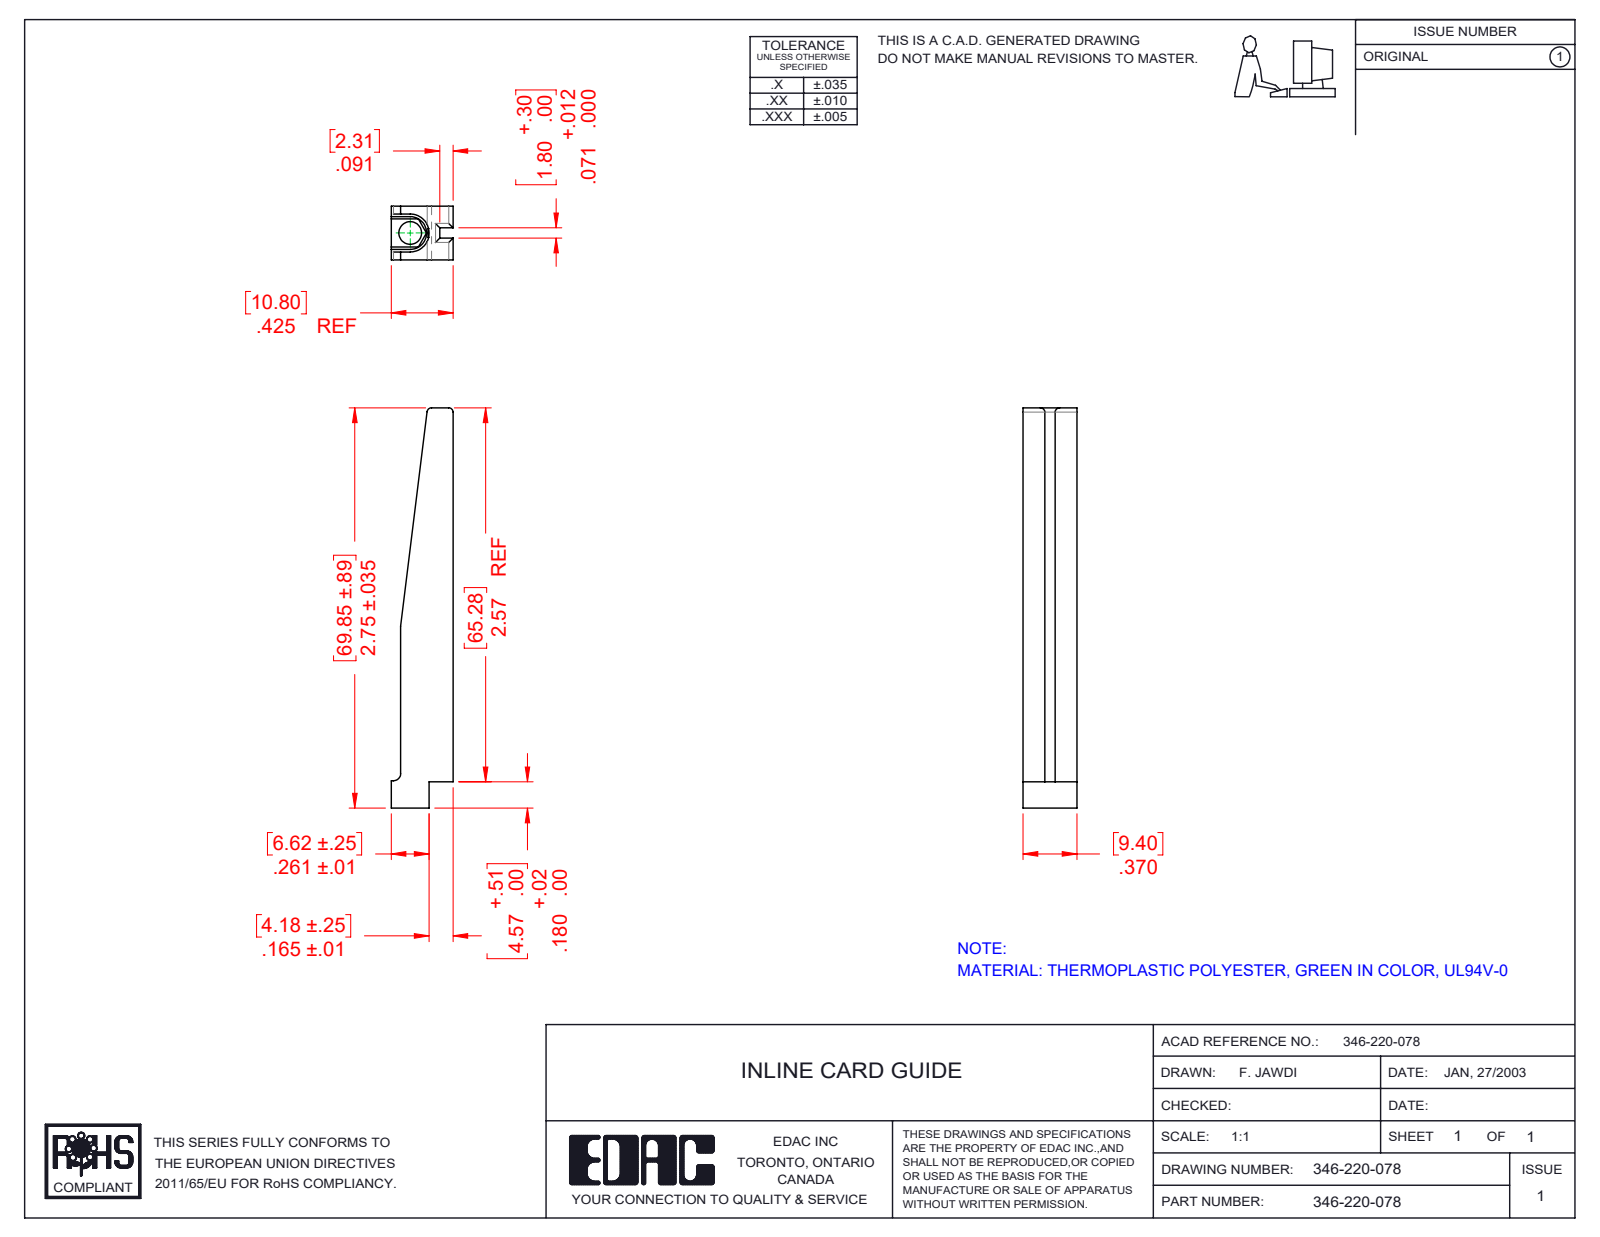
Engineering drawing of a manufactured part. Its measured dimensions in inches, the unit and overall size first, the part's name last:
Units: inches
Overall size (bounding box): 2.75 × 0.425 × 0.37
Round holes (diameter × count): ⌀0.156 ×1
Partial cylindrical surfaces — rounded edges, fillets, slot ends (radius × count): R0.03 ×5, R0.05 ×1, R0.112 ×1, R0.13 ×1
Main face-to-face distances: 0.37, 0.15, 0.22, 0.071, 0.091, 0.055, 0.315, 0.095, 0.166, 0.261
Volume: 0.209 in³ · Surface area: 4.96 in²
Bodies: 1 solid, 94 faces (62 planar, 14 cylindrical, 18 other)
Part name (STEP PRODUCT): 346-220-078
STEP written by: SolidWorks 2020 (AUTOMOTIVE_DESIGN)
